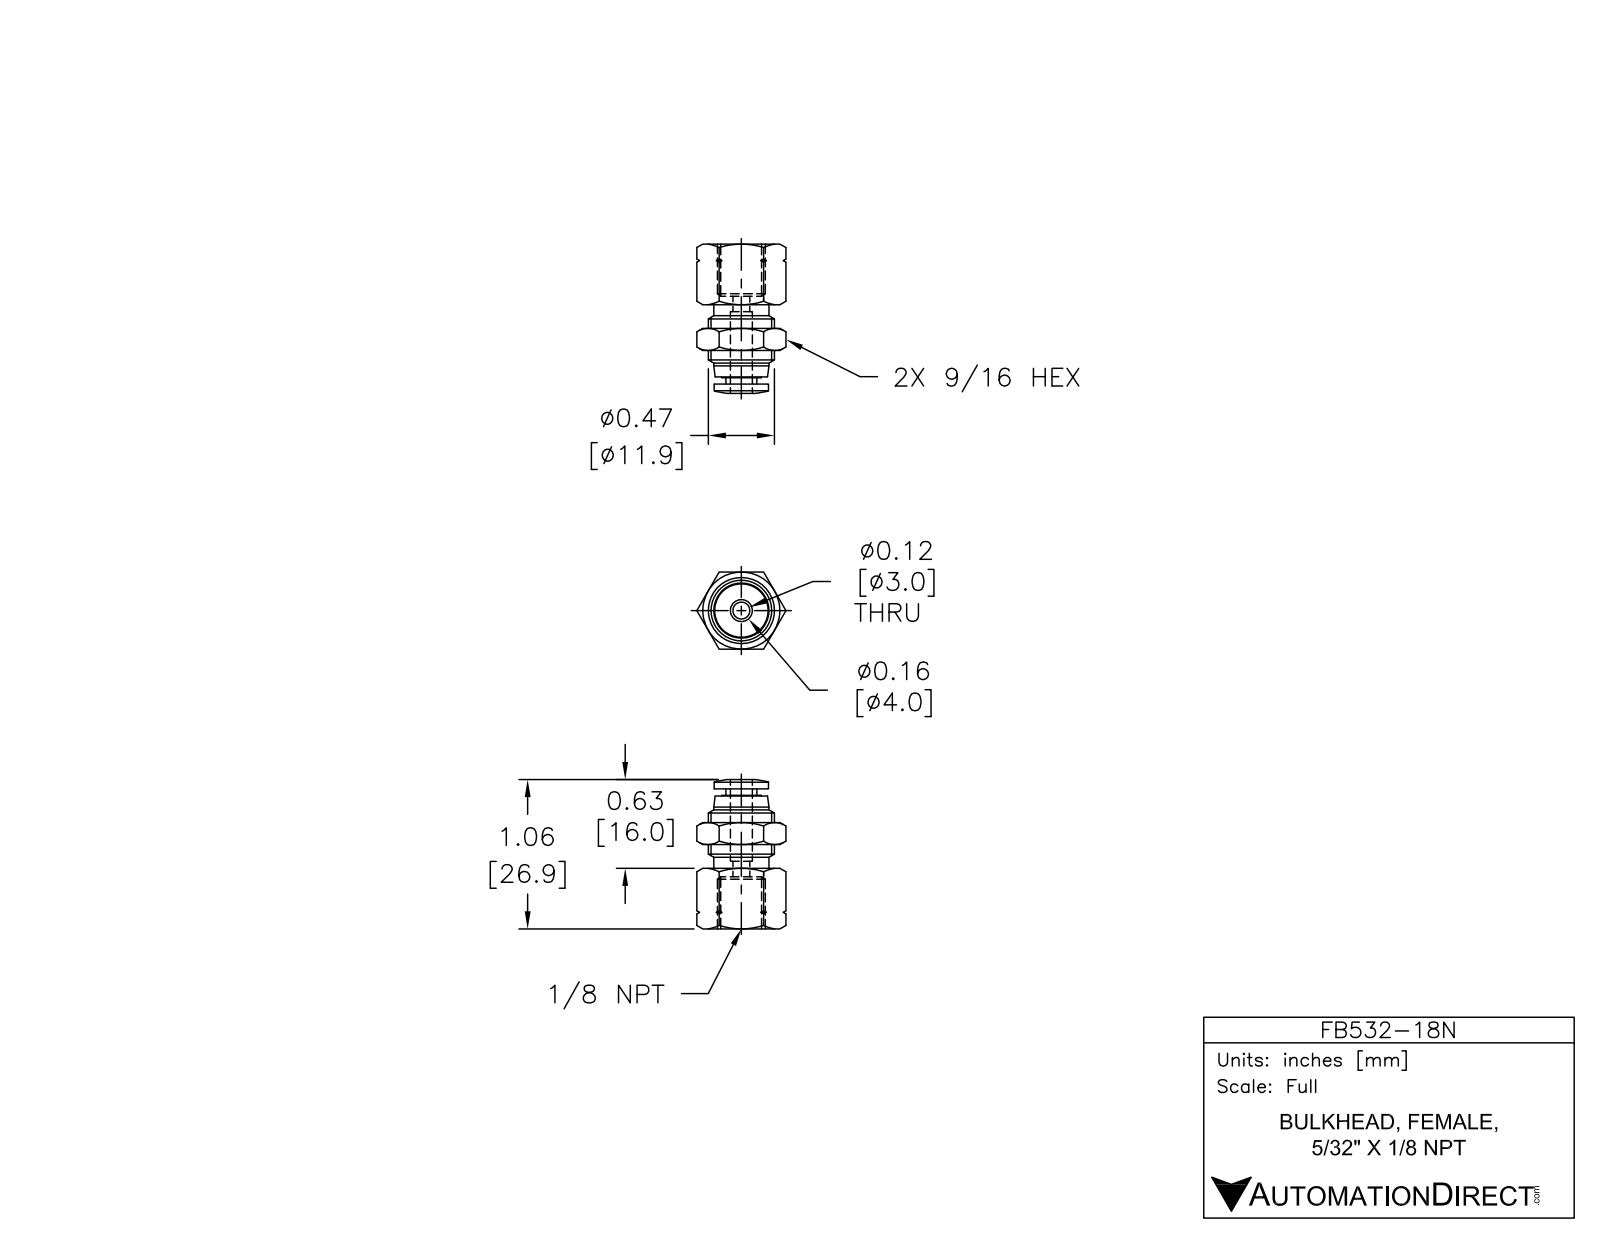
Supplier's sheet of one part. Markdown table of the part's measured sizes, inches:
| quantity | value |
| --- | --- |
| part name | FB532-18N |
| STEP written by | SolidWorks 2015 (AUTOMOTIVE_DESIGN) |
| units | inches |
| bodies | 1 solid, 91 faces (21 planar, 18 cylindrical, 52 other) |
| overall size | 1.067 × 0.636 × 0.551 |
| volume | 0.157 in³ |
| surface area | 3.35 in² |
| round holes (diameter × count) | 0.118 × 1, 0.169 × 1 |
| round bosses / shafts (diameter × count) | 0.472 × 1, 0.394 × 1, 0.388 × 1, 0.283 × 1, 0.22 × 1 |
| main face-to-face distances | 0.551, 0.433, 0.374, 0.059, 1, 0.626, 0.567, 0.593, 0.219, 0.159 |
